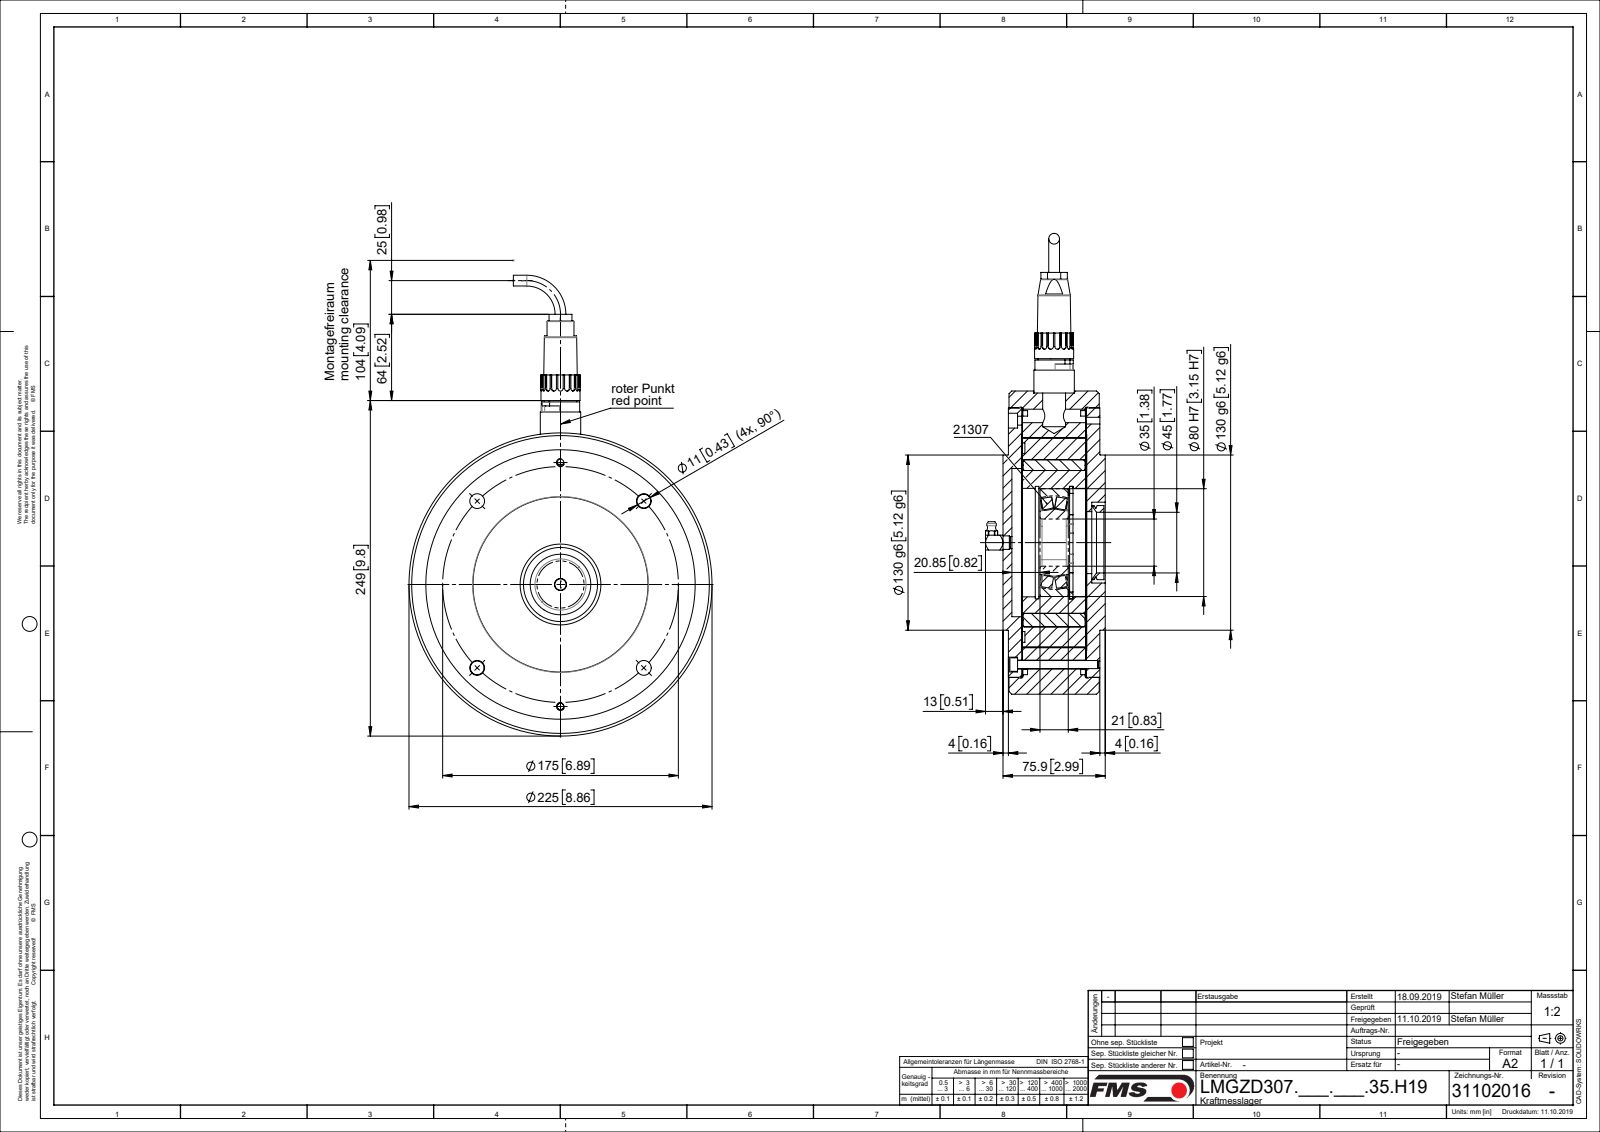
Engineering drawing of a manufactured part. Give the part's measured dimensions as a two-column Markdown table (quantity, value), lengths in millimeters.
| quantity | value |
| --- | --- |
| part name | Flanschstecker_Kunstst_7Pol_01; 49027_01; Si-Ring DIN472_D80x2.5; 48072_01 (+8 more) |
| STEP written by | SolidWorks 2018 (CONFIG_CONTROL_DESIGN) |
| units | millimeters |
| bodies | 50 solids, 856 faces (239 planar, 344 cylindrical, 273 other) |
| overall size | 342 × 225 × 88.9 |
| volume | 2 433 000 mm³ |
| surface area | 456 624 mm² |
| round holes (diameter × count) | 11 × 6, 2.5 × 4, 3 × 2, 3.4 × 2, 3.6 × 2, 5 × 2, 6.6 × 2, 10 × 2, 10.2 × 2, 8 × 1, 9 × 1, 10.5 × 1 |
| round bosses / shafts (diameter × count) | 2.15 × 7, 10 × 2, 5.5 × 2, 3 × 2, 225 × 1, 199 × 1, 188 × 1, 140 × 1 |
| partial cylindrical surfaces (radius × count) | 2 × 17, 0.1 × 4, 11 × 4, 3 × 2, 4.91 × 2, 4.5 × 1, 33.25 × 1, 79 × 1 |
| main face-to-face distances | 47.25, 10.2, 10.45, 57.45, 57.7, 48, 0.75, 0.5, 47.75, 9.7 |
| hole center spacings | 16.26, 22.47, 23, 62.02, 68.17, 87.5, 123.74, 134.45 |
